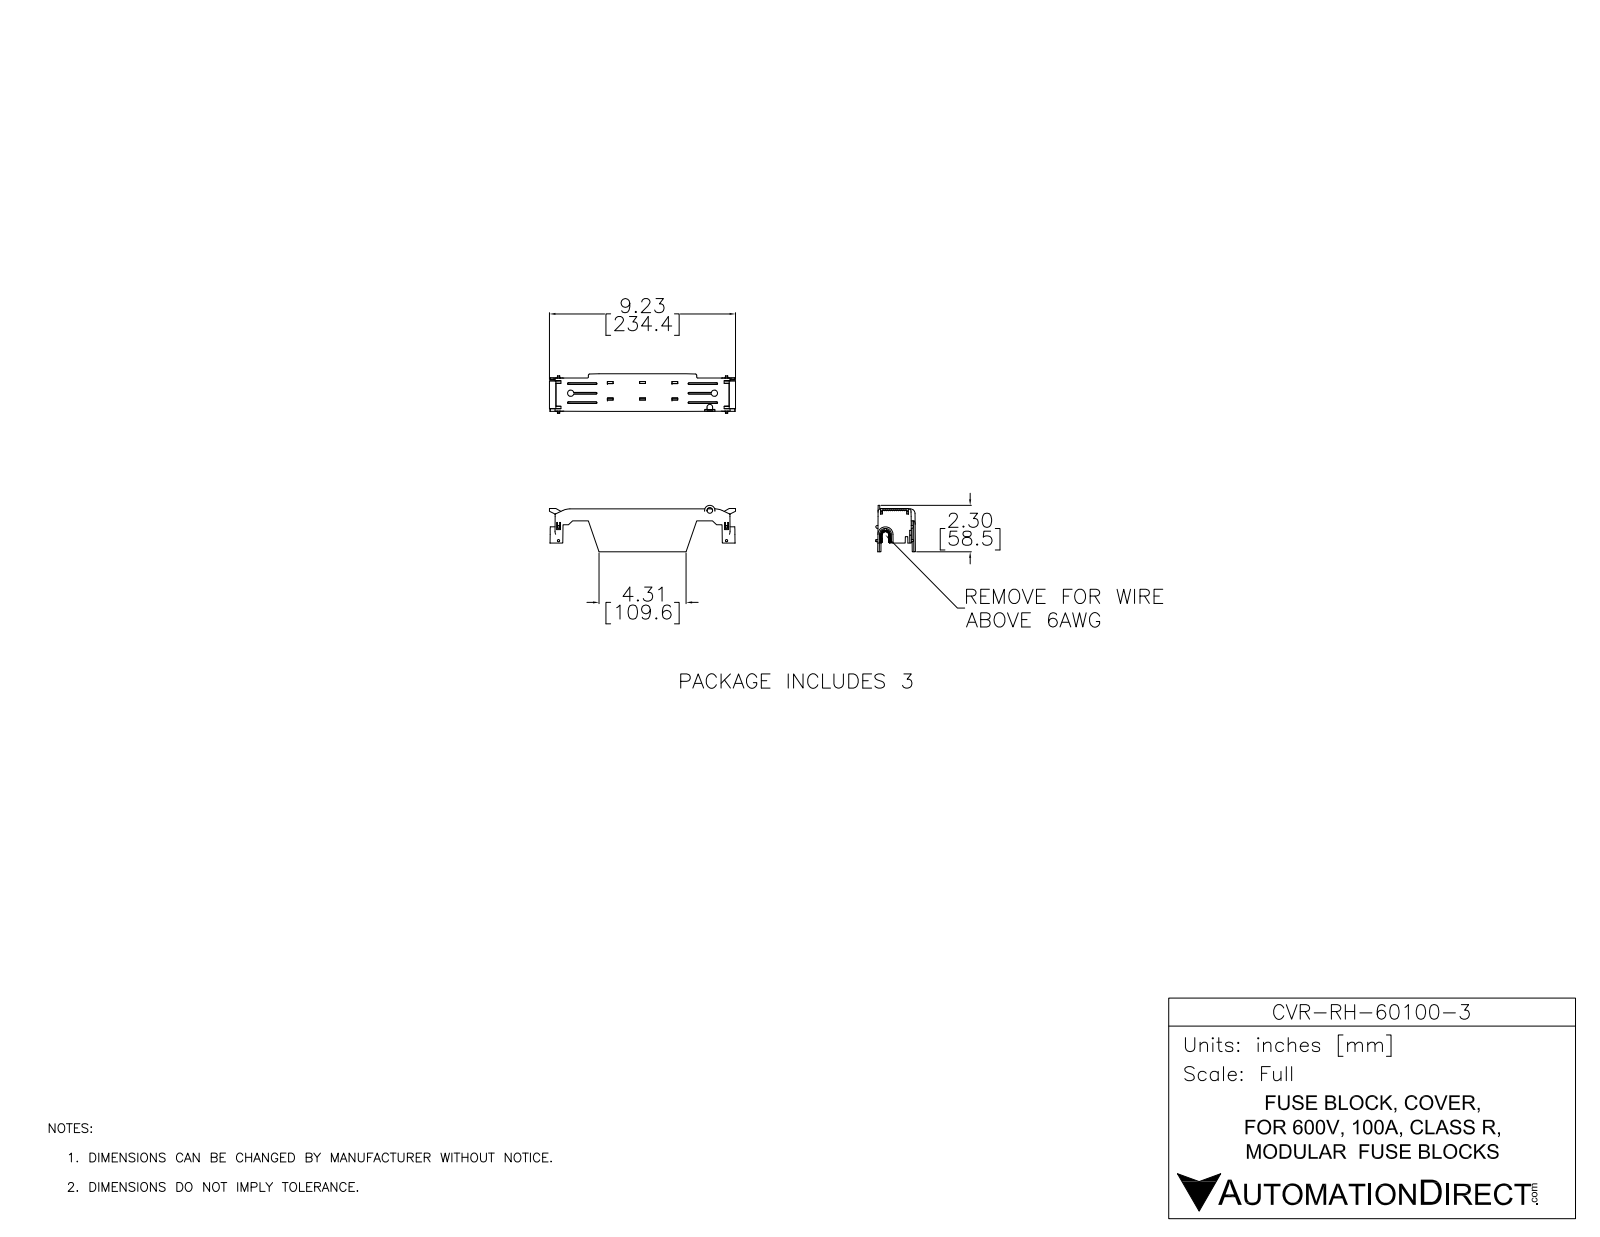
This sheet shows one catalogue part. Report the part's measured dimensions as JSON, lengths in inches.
{"part_name": "CVR-RH-60100-3", "step_written_by": "SolidWorks 2017 (AUTOMOTIVE_DESIGN)", "units": "inches", "bodies": {"solids": 1, "faces": 1436, "planar": 948, "cylindrical": 102, "other": 386}, "overall_size": [9.23, 2.304, 1.964], "volume_in3": 4.09, "surface_area_in2": 110.1, "round_holes": [[0.276, 1]], "partial_cylinders_radius": [[0.039, 18], [0.118, 14], [0.031, 6], [0.059, 4], [0.01, 2], [0.02, 2], [0.167, 2], [0.63, 2]], "face_to_face_distances": [0.079, 0.197, 0.118, 0.276, 0.157, 0.803, 0.989, 1.068, 1.186, 1.265]}
